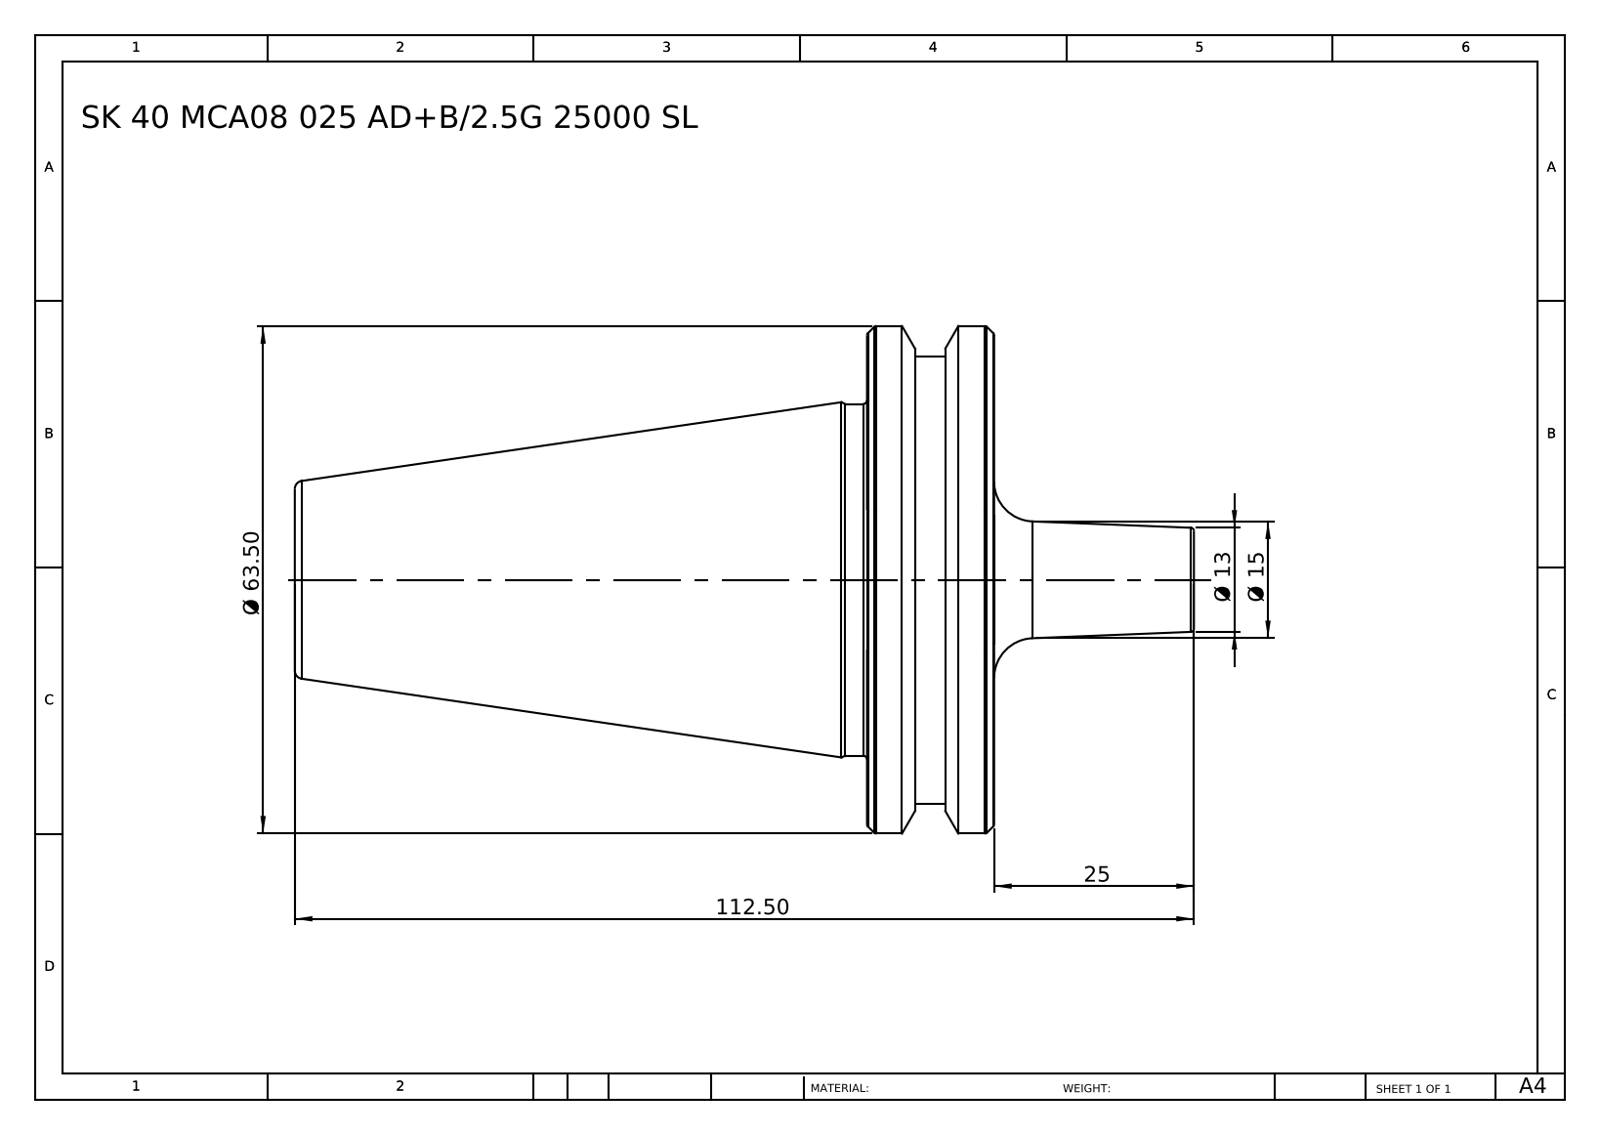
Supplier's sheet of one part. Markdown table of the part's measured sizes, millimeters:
| quantity | value |
| --- | --- |
| part name | SK 40 MCA08 025 AD+B-2.5G 25000 SL |
| STEP written by | SolidWorks 2014 (CONFIG_CONTROL_DESIGN) |
| units | millimeters |
| bodies | 1 solid, 64 faces (6 planar, 8 cylindrical, 50 other) |
| overall size | 112.5 × 63.5 × 63.5 |
| volume | 121 216 mm³ |
| surface area | 17 896 mm² |
| round bosses / shafts (diameter × count) | 63.5 × 1, 56 × 1, 44 × 1 |
| main face-to-face distances | 15.9, 87.5, 71.6, 6.1, 9.8, 81.4, 9.9, 3.8, 6, 77.6 |
